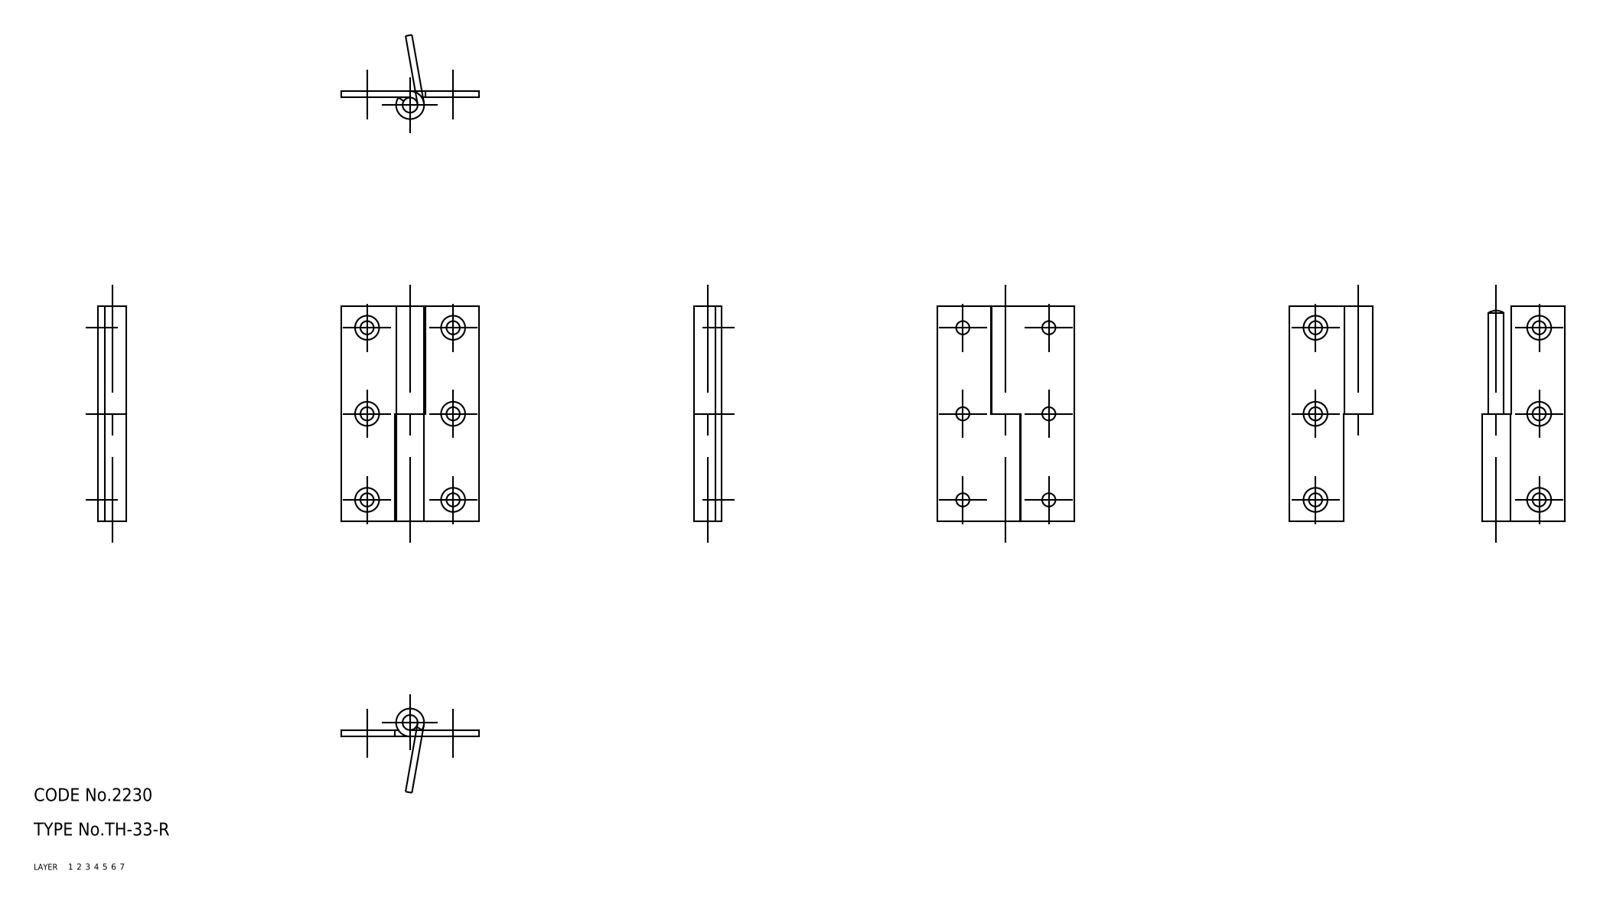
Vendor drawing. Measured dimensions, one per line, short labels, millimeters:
name: shaft; hinge piece_B; hinge piece_A; TH_33_R_8128_36
written by: CADfix (AUTOMOTIVE_DESIGN)
unit: mm
bodies: 3 solids, 48 faces (0 planar, 0 cylindrical, 48 other)
size: 50 × 32 × 6.5
volume: 3 469 mm³; area: 5 161 mm²
